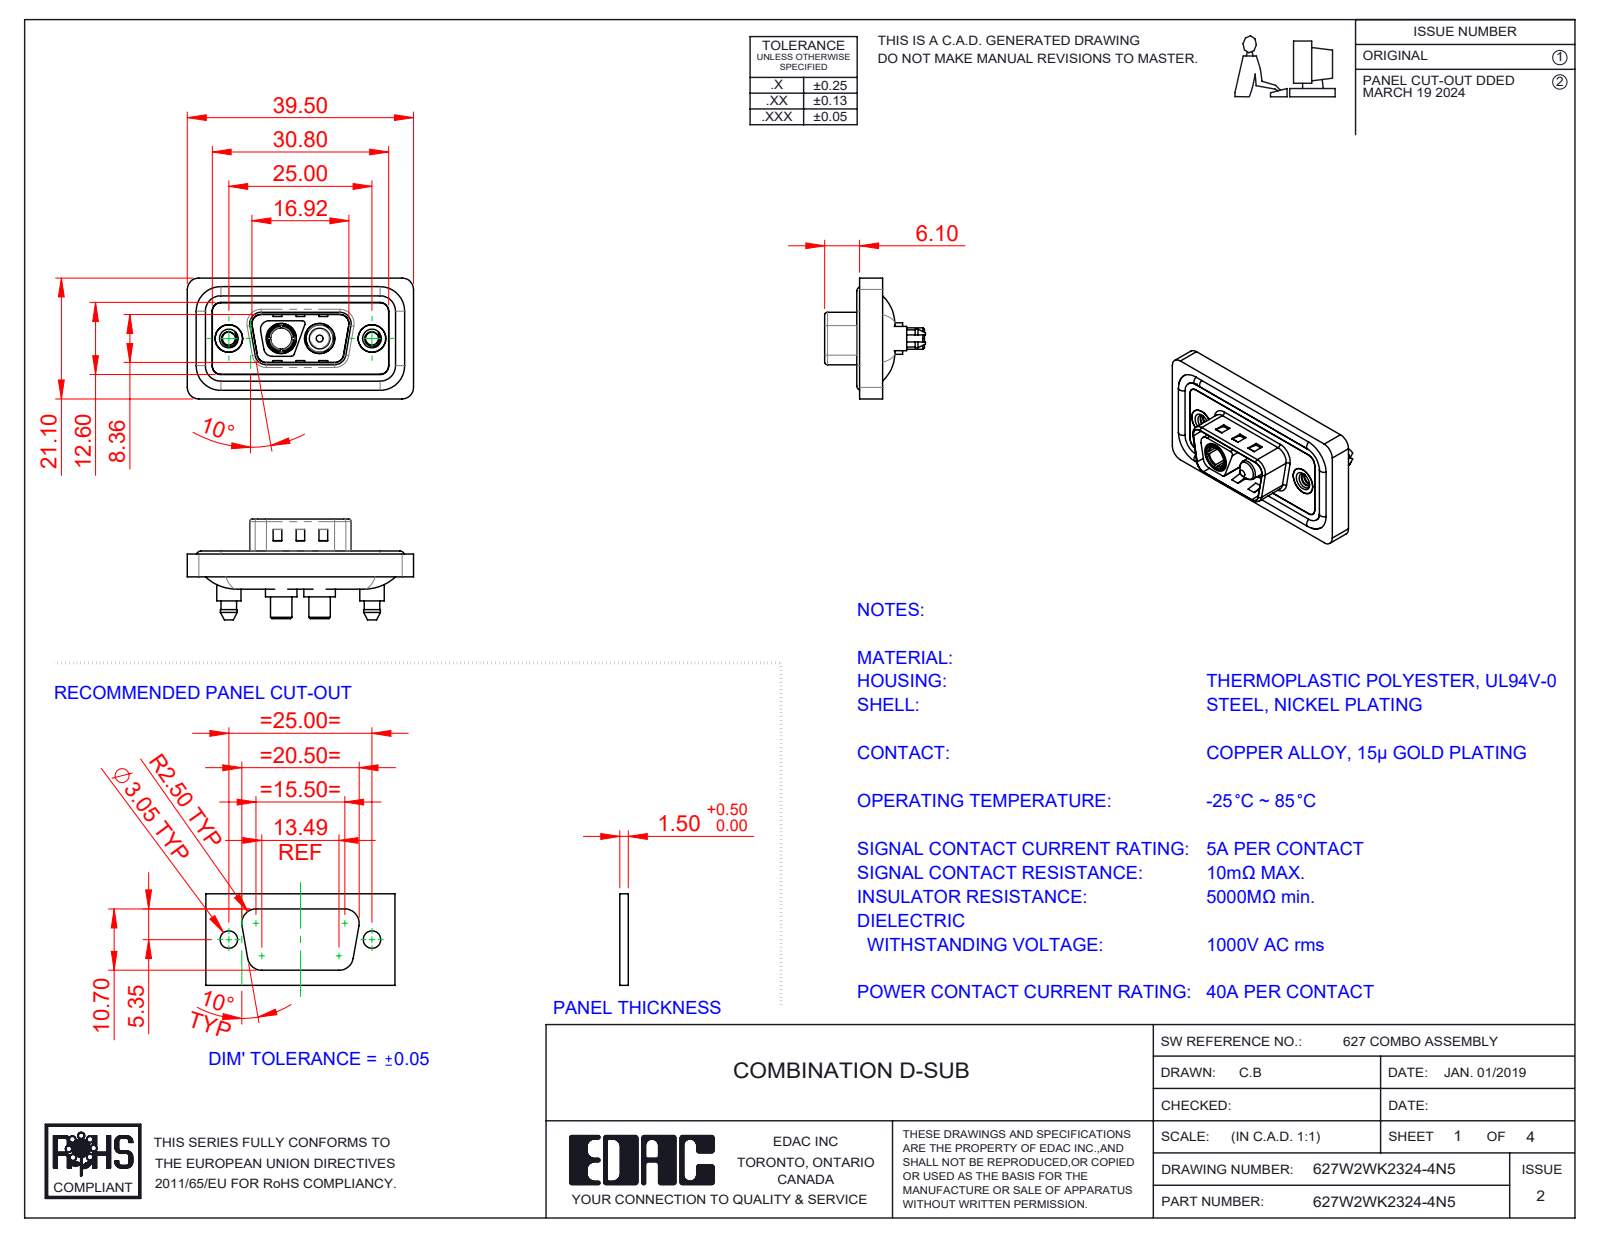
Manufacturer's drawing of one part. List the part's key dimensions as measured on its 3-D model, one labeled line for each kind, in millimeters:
Part name (STEP PRODUCT): Power Socket_40A S; 627Combo Threaded Boardlock_5; 627Combo Housing_2WK2; Power Pin_40A S (+4 more)
STEP written by: SolidWorks 2023 (CONFIG_CONTROL_DESIGN)
Units: millimetres
Bodies: 11 solids, 584 faces (205 planar, 259 cylindrical, 120 other)
Overall size (bounding box): 39.5 × 21.1 × 17.6
Volume: 4 725 mm³ · Surface area: 7 697 mm²
Round holes (diameter × count): ⌀2.26 ×2, ⌀4 ×2, ⌀4.8 ×2, ⌀4.85 ×2, ⌀5 ×2, ⌀5.3 ×2, ⌀3.7 ×1
Round bosses / shafts (diameter × count): ⌀1.6 ×4, ⌀5.5 ×2, ⌀5.4 ×2, ⌀5.2 ×2, ⌀4.9 ×2, ⌀4.75 ×2, ⌀4.25 ×2, ⌀3.75 ×2
Partial cylindrical surfaces — rounded edges, fillets, slot ends (radius × count): R1.5 ×26, R2 ×18, R0.5 ×10, R1.6 ×10, R0.25 ×4, R0.6 ×4, R0.65 ×4, R0.9 ×4
Main face-to-face distances: 0.4, 1.1, 2.9, 3.1, 0.5, 1.6, 1.5, 4, 1.8, 3.2
Hole centre spacings: 9.14, 15.86, 6.72, 25
